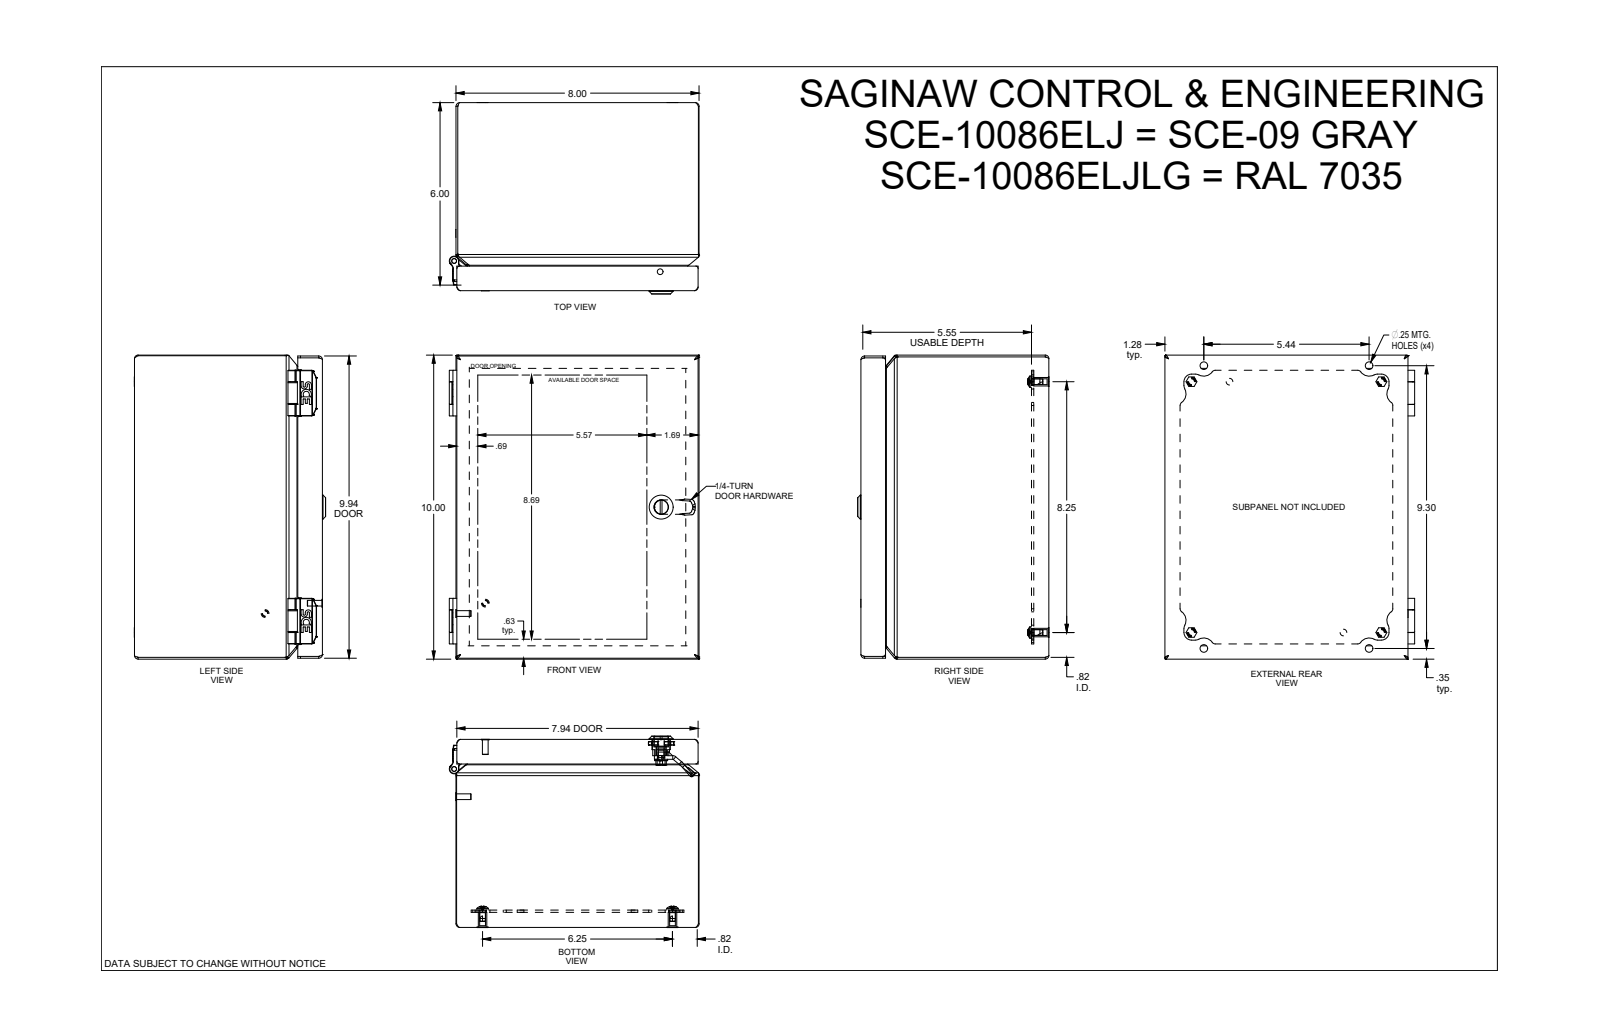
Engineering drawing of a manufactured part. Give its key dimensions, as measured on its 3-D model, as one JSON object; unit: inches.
{"part_name": "SCE-10086ELJ", "step_written_by": "SolidWorks 2019 (AUTOMOTIVE_DESIGN)", "units": "inches", "bodies": {"solids": 30, "faces": 921, "planar": 355, "cylindrical": 302, "other": 264}, "overall_size": [9.999, 8.22, 6.296], "volume_in3": 31.53, "surface_area_in2": 993.7, "round_holes": [[0.19, 4], [0.25, 4], [0.284, 4], [0.02, 2], [0.1, 2], [0.218, 2], [0.158, 1], [0.2, 1], [0.239, 1], [0.254, 1], [0.269, 1], [0.282, 1]], "round_bosses_or_shafts": [[0.188, 6], [0.373, 4], [0.28, 4], [0.16, 4], [0.26, 2], [0.256, 2], [0.237, 2], [0.23, 2]], "partial_cylinders_radius": [[0.03, 28], [0.05, 24], [0.013, 21], [0.25, 13], [0.125, 11], [0.01, 10], [0.344, 8], [0.024, 5]], "face_to_face_distances": [0.059, 6.128, 7.941, 9.94, 6.187, 6.069, 0.571, 0.512, 5.557, 5.616], "hole_center_spacings": [6.25, 6.25, 10.35, 1.25, 5, 4.142, 7.18, 8.249]}
